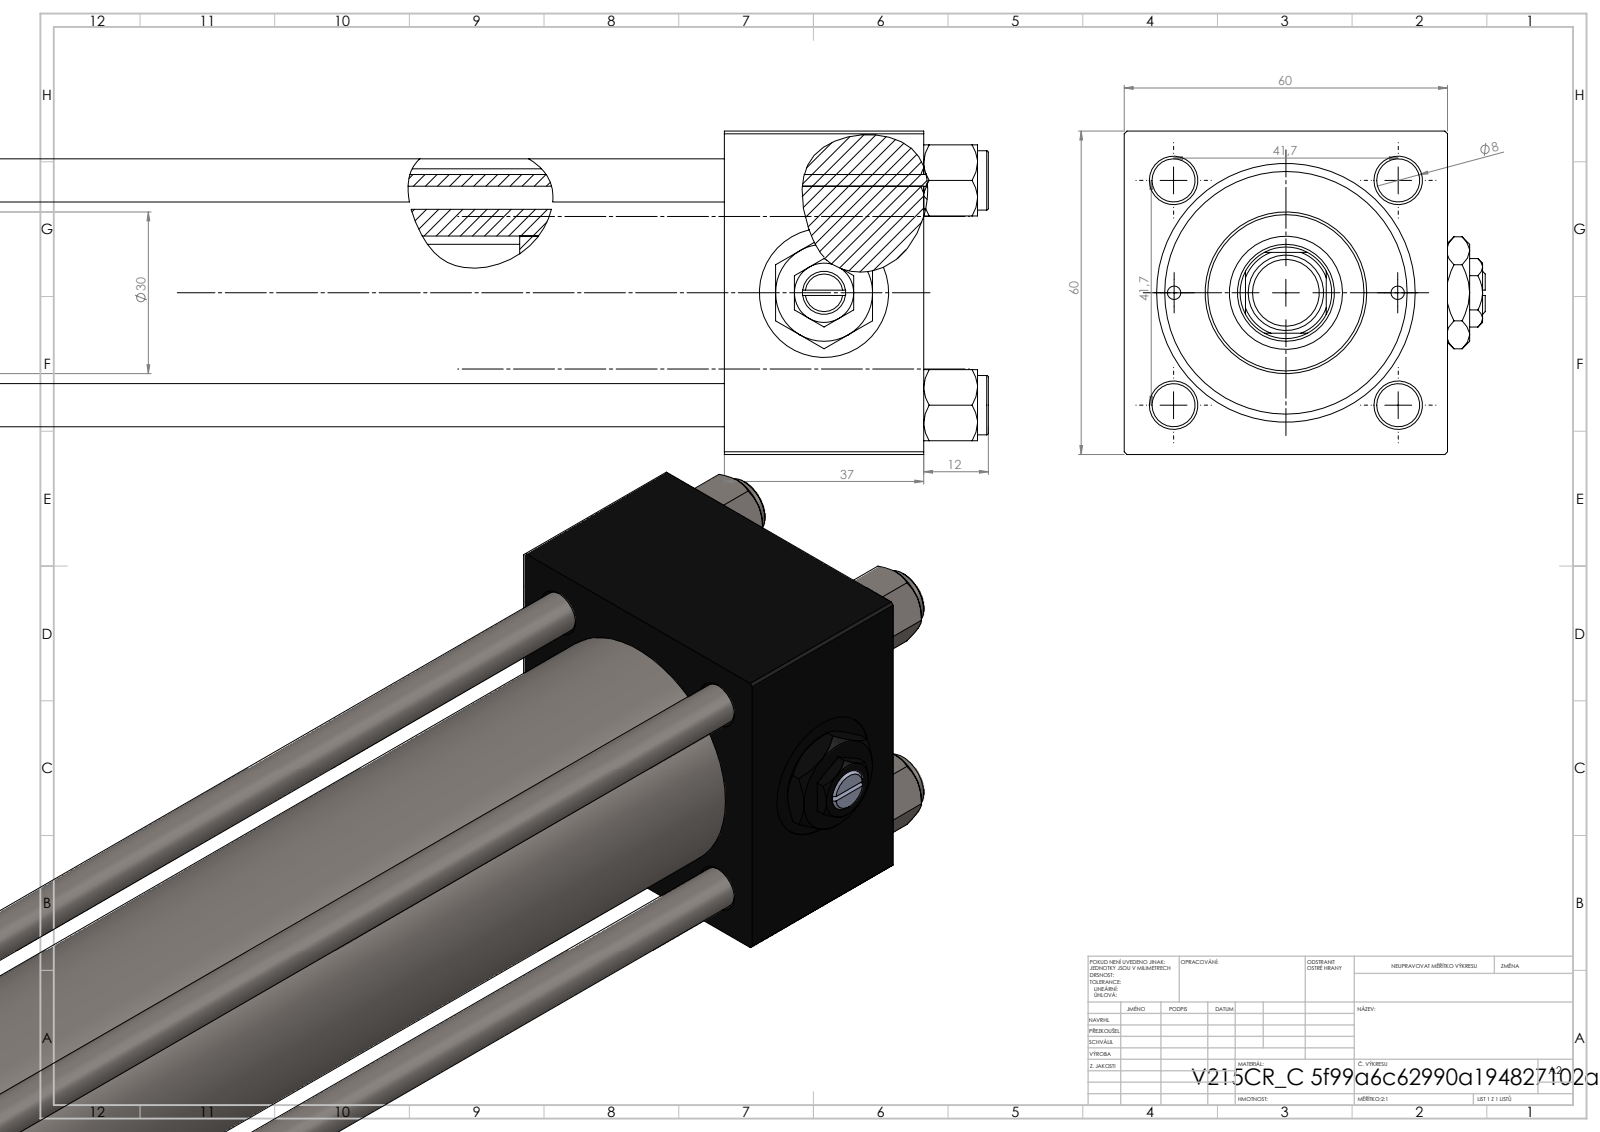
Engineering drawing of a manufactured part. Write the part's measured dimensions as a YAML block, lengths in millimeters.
part_name: "NUT_M5_C; V215_VC_A; Zatka_pro_OIL_PORT; V215CR_C_TYCINKA (+3 more)"
step_written_by: "SolidWorks 2019 (CONFIG_CONTROL_DESIGN)"
units: millimeters
bodies: {solids: 14, faces: 1270, planar: 580, cylindrical: 106, other: 584}
overall_size: [343, 67, 60]
volume: 522457
surface_area: 169269
round_holes:
  - {diameter: 8, count: 4}
  - {diameter: 2.5, count: 2}
  - {diameter: 7, count: 2}
  - {diameter: 16.66, count: 2}
  - {diameter: 24, count: 2}
  - {diameter: 8.5, count: 1}
  - {diameter: 18, count: 1}
  - {diameter: 21, count: 1}
  - {diameter: 31, count: 1}
  - {diameter: 40, count: 1}
  - {diameter: 45, count: 1}
round_bosses_or_shafts:
  - {diameter: 11, count: 4}
  - {diameter: 46, count: 1}
  - {diameter: 30, count: 1}
  - {diameter: 14, count: 1}
  - {diameter: 12, count: 1}
partial_cylinders:
  - {radius: 8.5, count: 1}
face_to_face_distances: [60, 37, 288, 251, 53, 235, 198, 259.3, 222.3, 24.3]
hole_center_spacings: [20.85, 29.49, 41.7, 46.53, 20.75, 58.97, 41.5, 232.5]
